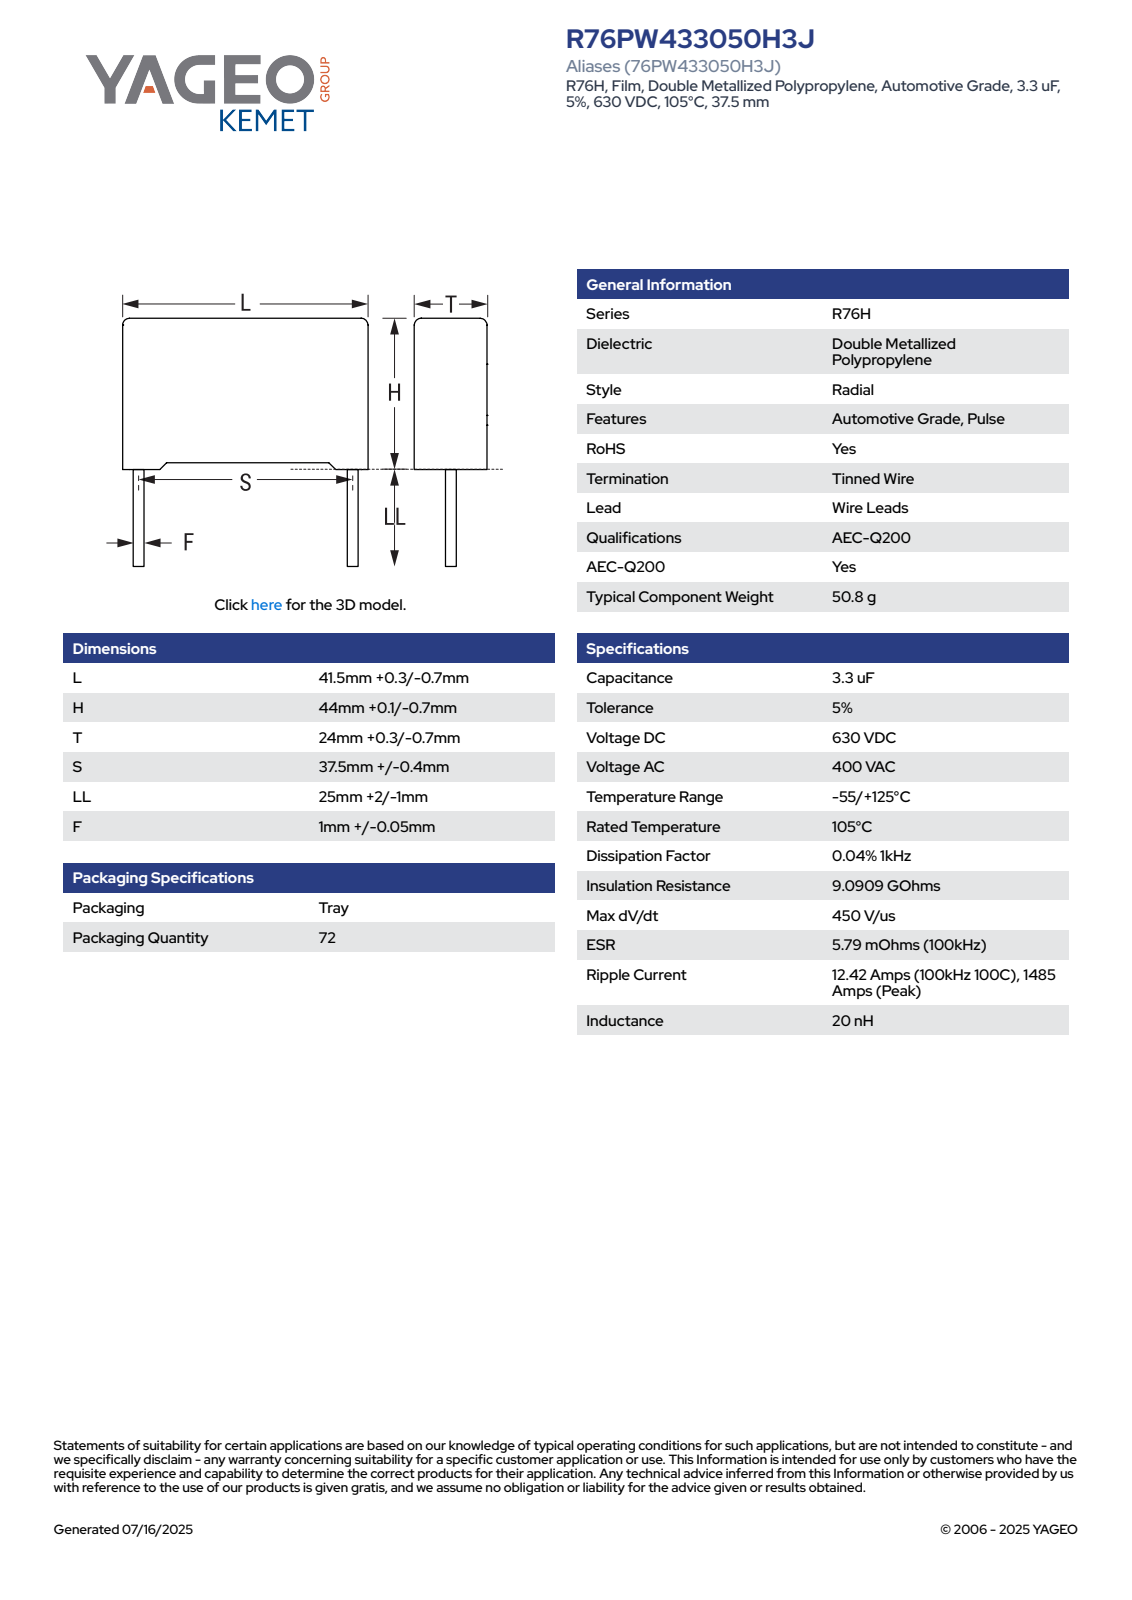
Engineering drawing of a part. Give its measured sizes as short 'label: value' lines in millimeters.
name: CFR_RB2R76_41.5X44X24_L41.8H44.1T24.3S37.5LL27F1.05
written by: SolidWorks 2014 (AUTOMOTIVE_DESIGN)
unit: mm
bodies: 4 solids, 85 faces (77 planar, 8 cylindrical, 0 other)
size: 71.1 × 41.8 × 24.3
volume: 43 522 mm³; area: 8 106 mm²
bosses: 2× ⌀1.05
rounds: 4× R0.5
face distances: 24.3, 41.8, 42.58, 0.77, 43.35, 0.75, 1.52, 44.1, 1.39, 40.41
